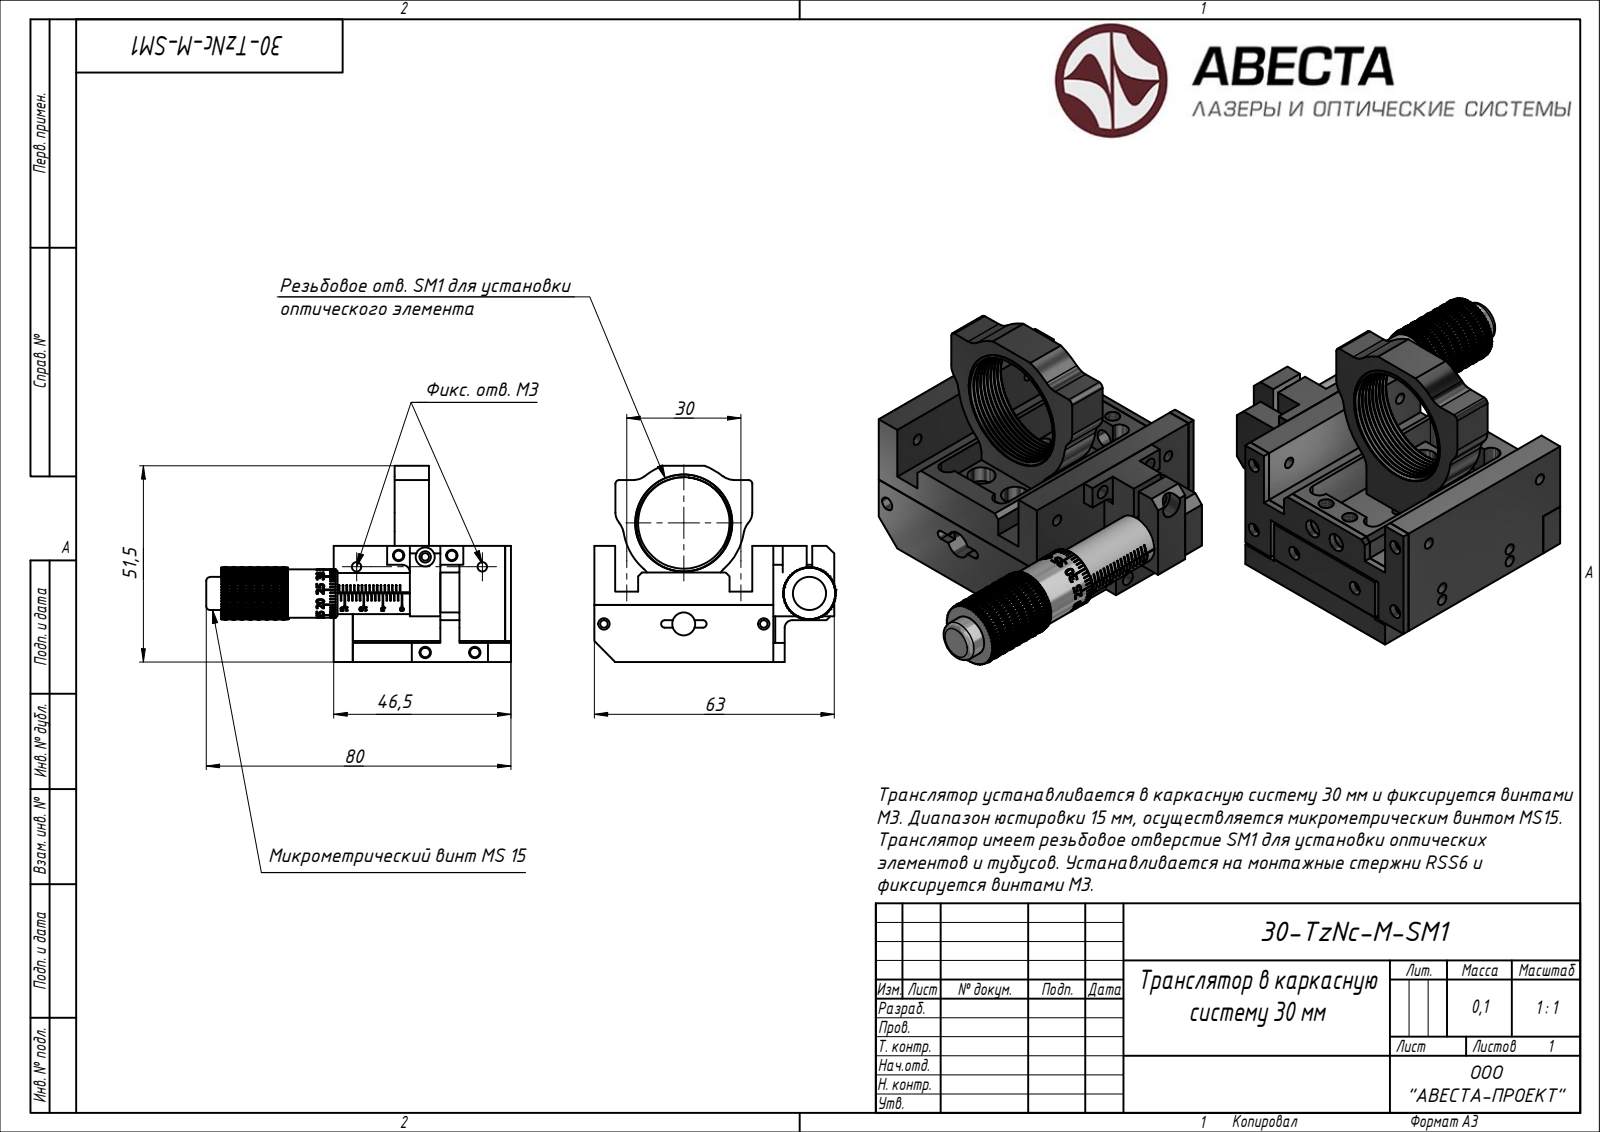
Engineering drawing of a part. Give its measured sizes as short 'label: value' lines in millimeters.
written by: Rhino 7.34 (AUTOMOTIVE_DESIGN)
unit: mm
bodies: 10 solids, 5223 faces (3625 planar, 1069 cylindrical, 529 other)
size: 105.79 × 63.45 × 59.5
volume: 85 009 mm³; area: 51 068 mm²
holes: 22× ⌀2.46, 11× ⌀3, 10× ⌀3.24, 7× ⌀6, 6× ⌀3.5, 5× ⌀2.01, 4× ⌀6.1, 2× ⌀2, 2× ⌀2.01, 2× ⌀2.46, 2× ⌀4, 2× ⌀6.14
bosses: 4× ⌀6, 2× ⌀3, 1× ⌀13.5, 1× ⌀12.7, 1× ⌀10.8, 1× ⌀9.5, 1× ⌀8.66, 1× ⌀2
rounds: 20× R0.12, 20× R0.3, 15× R2, 10× R0.14, 10× R0.14, 10× R0.16, 10× R0.16, 10× R0.18
face distances: 8, 5, 92, 0.5, 46.5, 5.5, 2, 13.5, 7, 1.5
hole spacings: 30, 15, 5, 12.97, 13.45, 13.93, 14.32, 17.85
